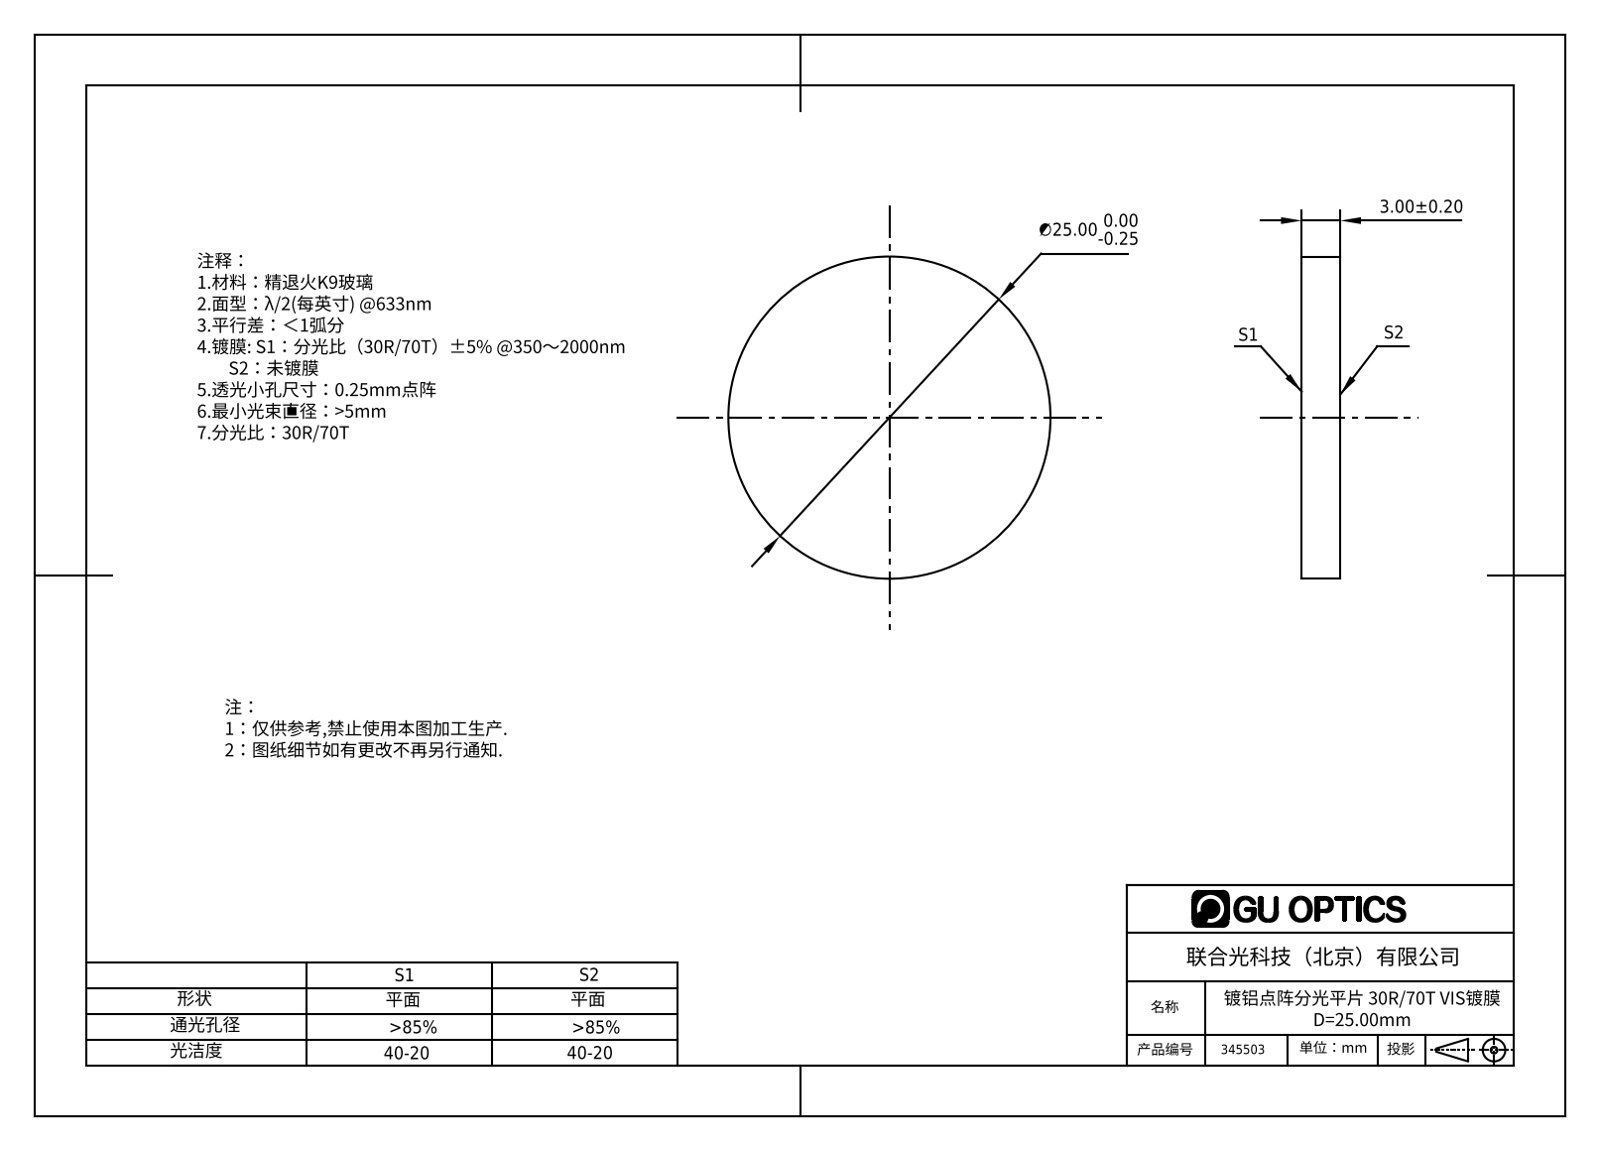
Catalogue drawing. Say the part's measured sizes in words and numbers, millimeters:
The part is named "345503". Its 3-D file was written by "SolidWorks 2016 (AUTOMOTIVE_DESIGN)". It is 1 solid with 4 faces: 2 planar, 2 cylindrical and 0 other. Overall it measures 25 by 25 by 3 millimeters. Its volume is 1 473 cubic millimeters and its surface area 1 217 square millimeters. Round bosses or shafts: 1 of diameter 25. The main face-to-face distances are 3.
